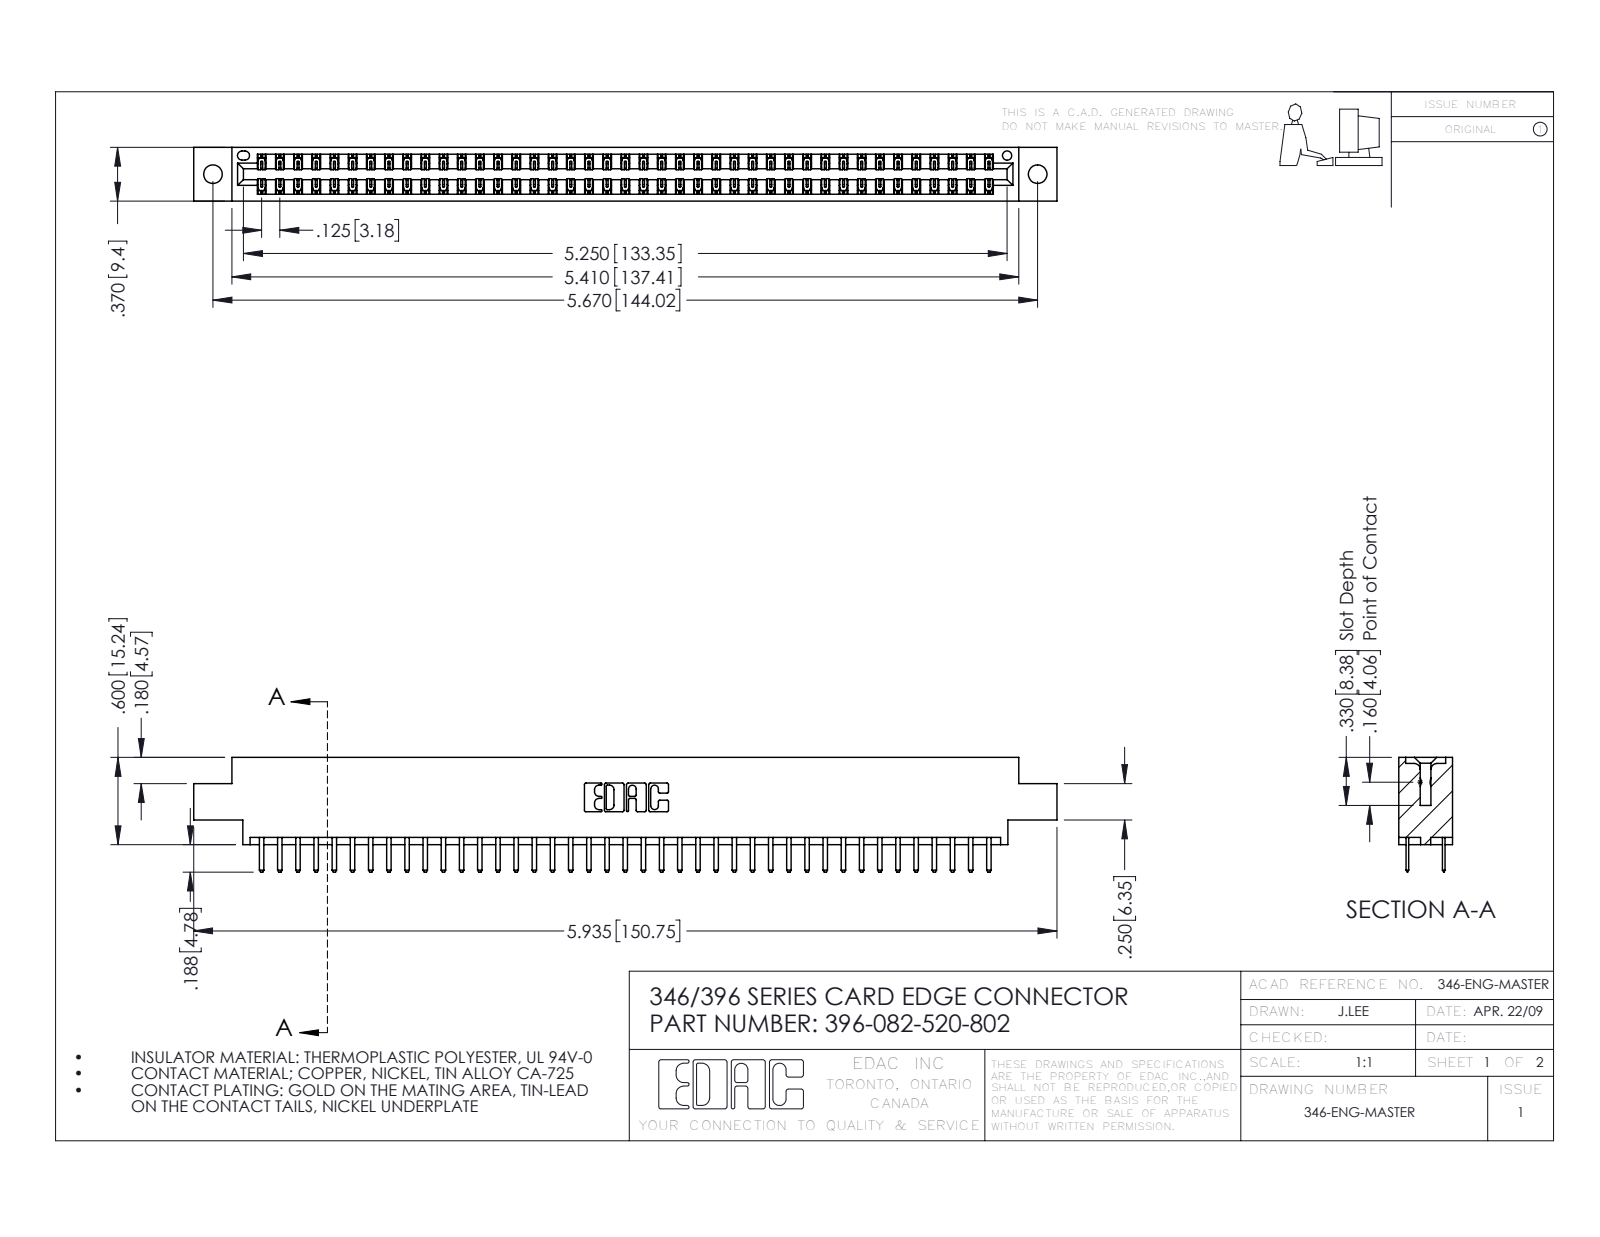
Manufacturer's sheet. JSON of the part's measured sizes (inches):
{"part_name": "345-292-001_345-293-120; 396-082-520-802; 346 Part_0.170 Offset - 0.128 Dia", "step_written_by": "SolidWorks 2016 (CONFIG_CONTROL_DESIGN)", "units": "inches", "bodies": {"solids": 83, "faces": 4718, "planar": 3114, "cylindrical": 1604, "other": 0}, "overall_size": [5.935, 0.788, 0.37], "volume_in3": 0.883, "surface_area_in2": 30.52, "round_holes": [[0.128, 2], [0.064, 1]], "partial_cylinders_radius": [[0.006, 123], [0.01, 86], [0.01, 22], [0.007, 6], [0.031, 6], [0.026, 3], [0.014, 2], [0.022, 2]], "face_to_face_distances": [0.048, 0.322, 0.37, 0.25, 0.275, 0.072, 0.298, 0.025, 0.148, 0.222], "hole_center_spacings": [0.246, 5.461, 5.67]}
